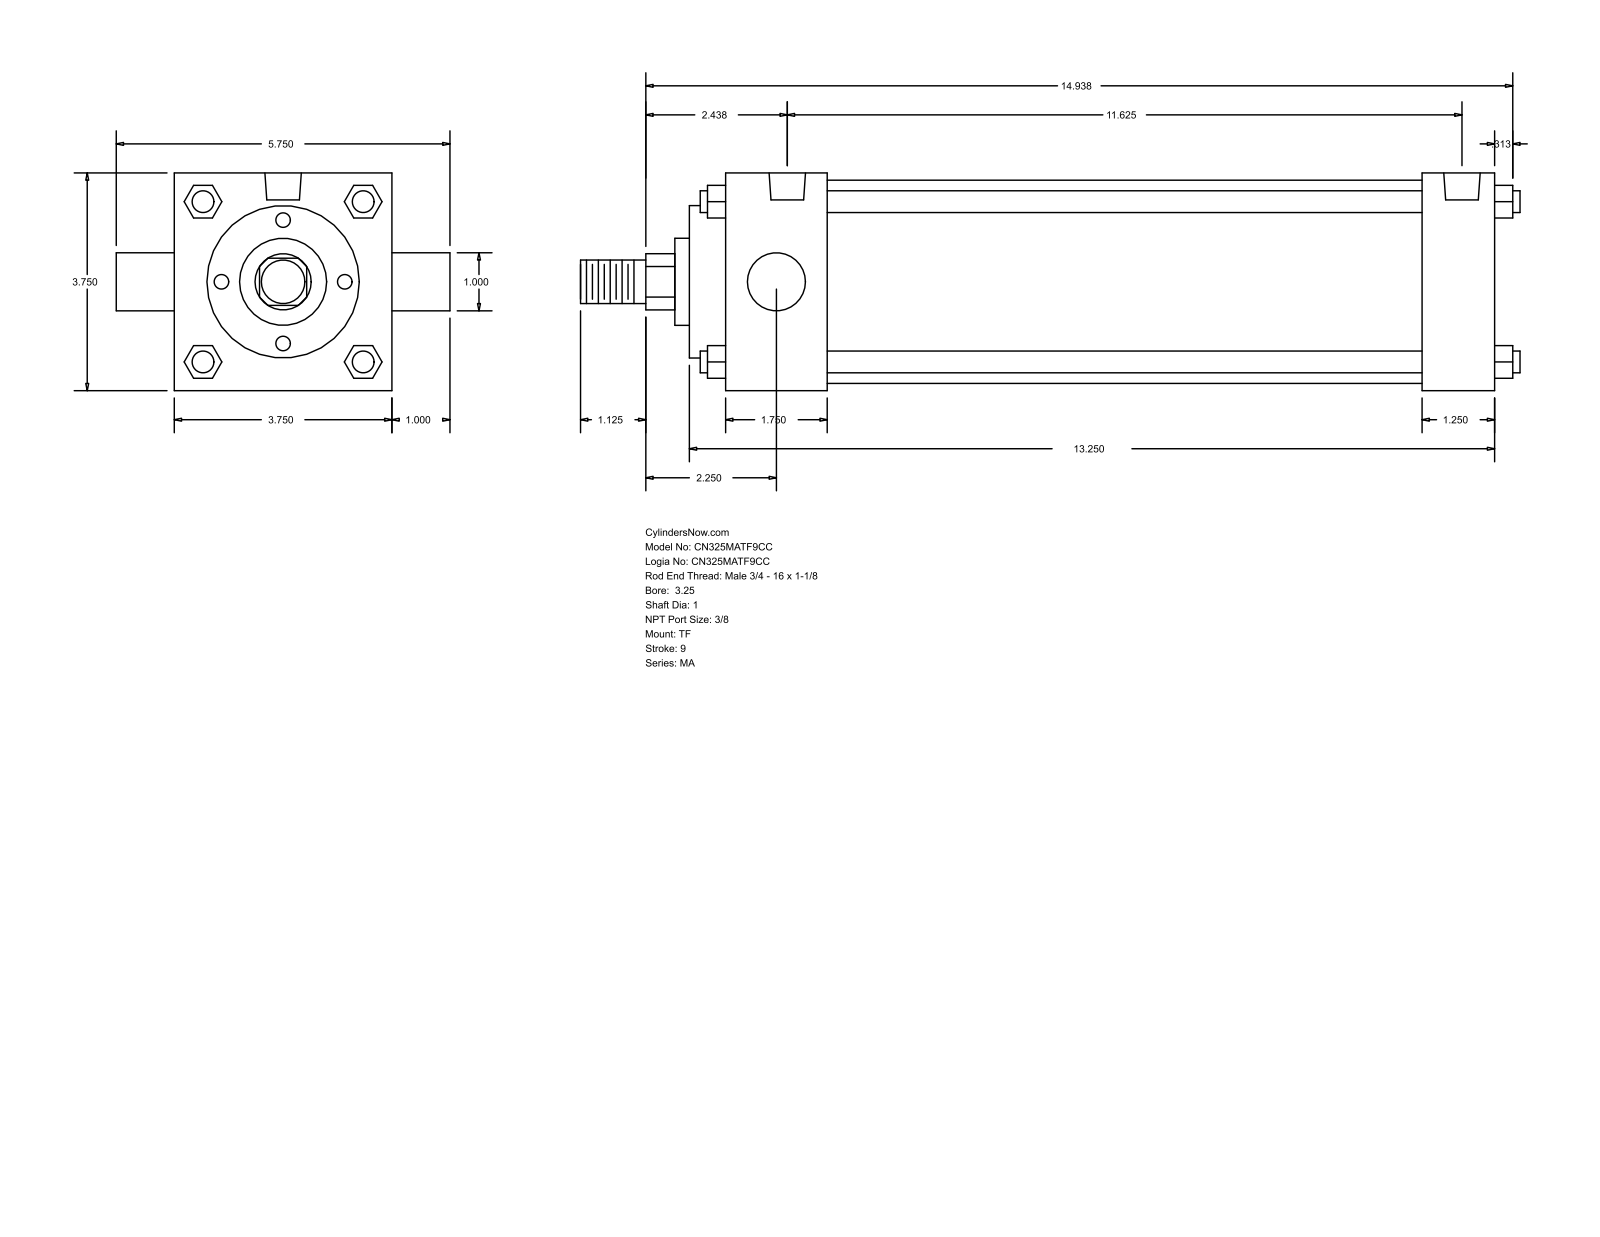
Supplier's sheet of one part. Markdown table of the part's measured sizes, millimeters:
| quantity | value |
| --- | --- |
| part name | MA_TF__0325_1 |
| STEP written by | GSSL Pune (CONFIG_CONTROL_DESIGN) |
| units | millimeters |
| bodies | 0 solids, 122 faces (93 planar, 29 cylindrical, 0 other) |
| overall size | 411.16 × 146.05 × 95.25 |
| round holes (diameter × count) | 11.11 × 3, 15.93 × 2 |
| round bosses / shafts (diameter × count) | 9.53 × 4, 25.4 × 2, 88.9 × 1, 66.67 × 1, 38.1 × 1, 19.05 × 1 |
| partial cylindrical surfaces (radius × count) | 12.29 × 1 |
| main face-to-face distances | 95.24, 336.56, 44.46, 304.81, 260.35, 292.1, 31.75, 15.87, 60.33, 320.68 |
| hole center spacings | 4.76, 290.52, 285.76, 295.28 |
